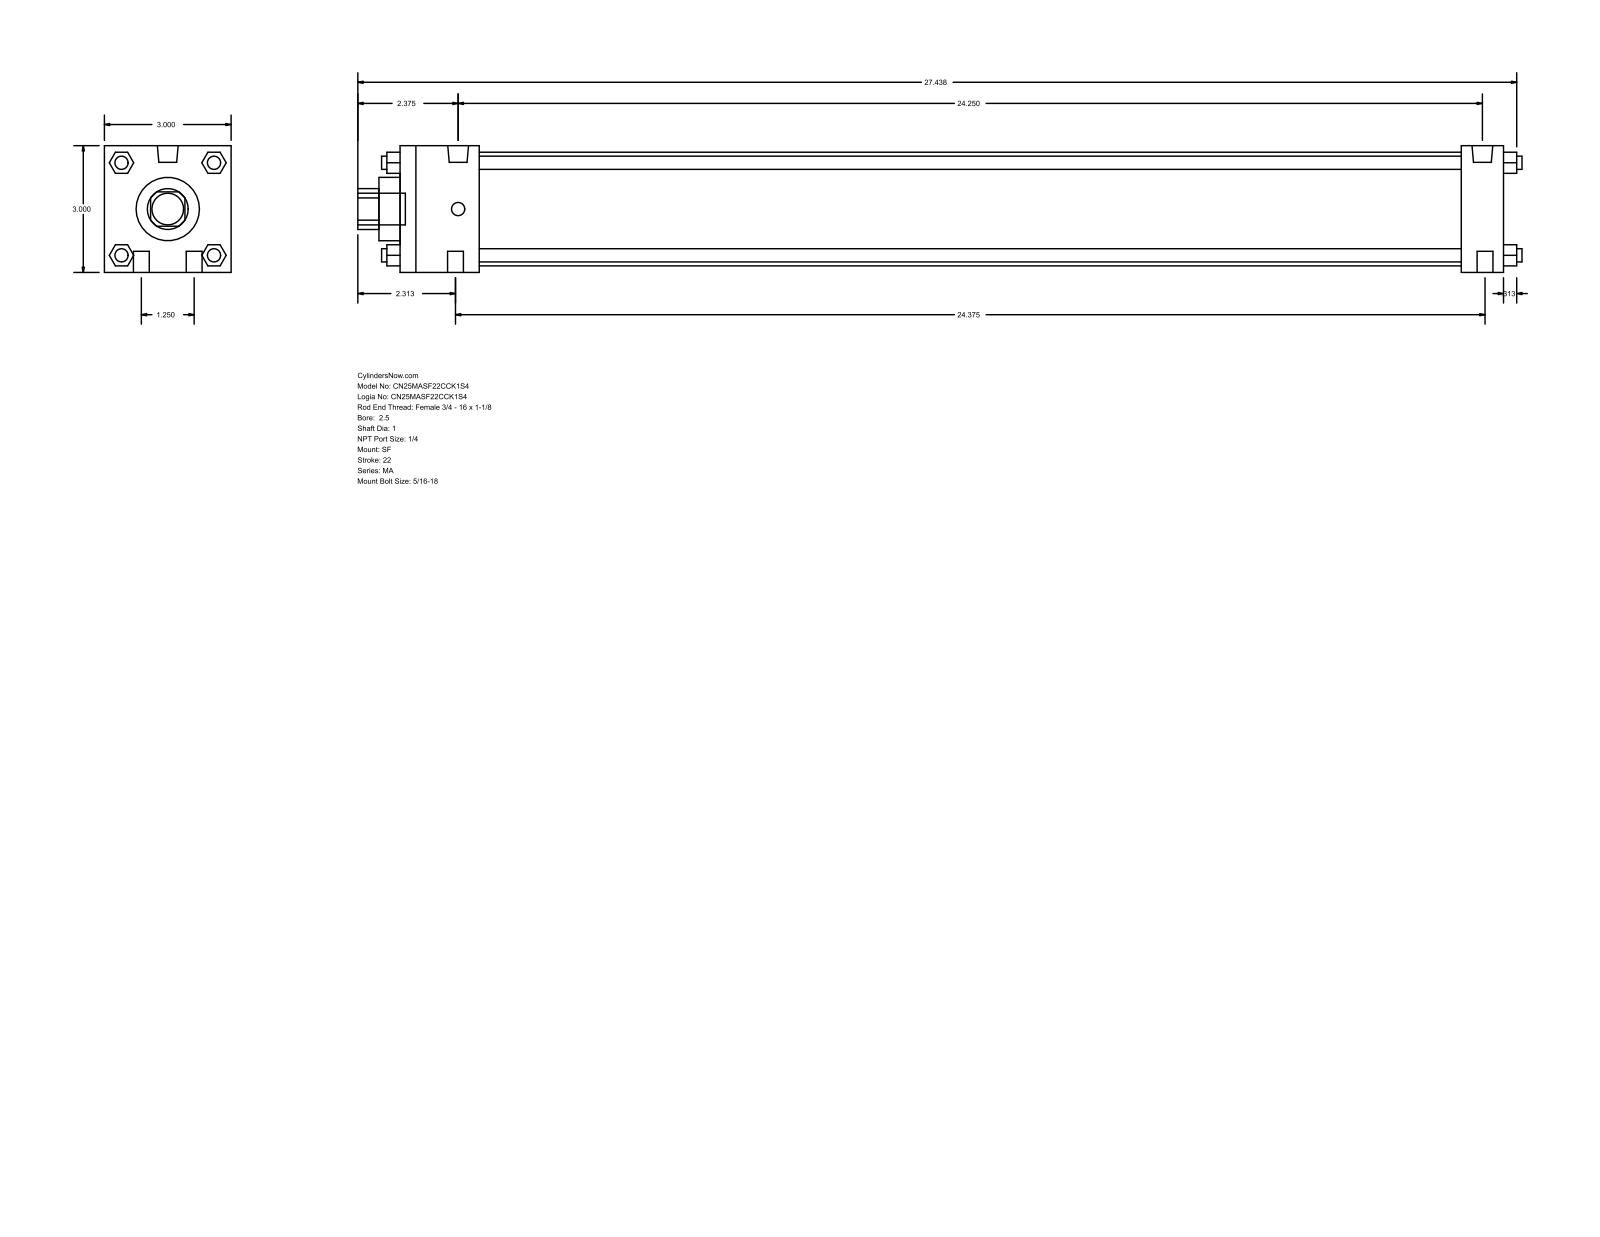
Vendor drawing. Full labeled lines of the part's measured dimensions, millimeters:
Part name (STEP PRODUCT): MA_SF__0250_1
STEP written by: GSSL Pune (CONFIG_CONTROL_DESIGN)
Units: millimetres
Bodies: 0 solids, 124 faces (94 planar, 30 cylindrical, 0 other)
Overall size (bounding box): 700.09 × 76.2 × 76.2
Round holes (diameter × count): ⌀25.4 ×1, ⌀38.1 ×1, ⌀68.33 ×1
Round bosses / shafts (diameter × count): ⌀7.94 ×6, ⌀9.53 ×4, ⌀12.49 ×2, ⌀19.05 ×1
Partial cylindrical surfaces — rounded edges, fillets, slot ends (radius × count): R12.29 ×1
Main face-to-face distances: 76.2, 663.58, 12.7, 25.4, 638.18, 47.63, 590.55, 615.95, 27.81, 48.17
